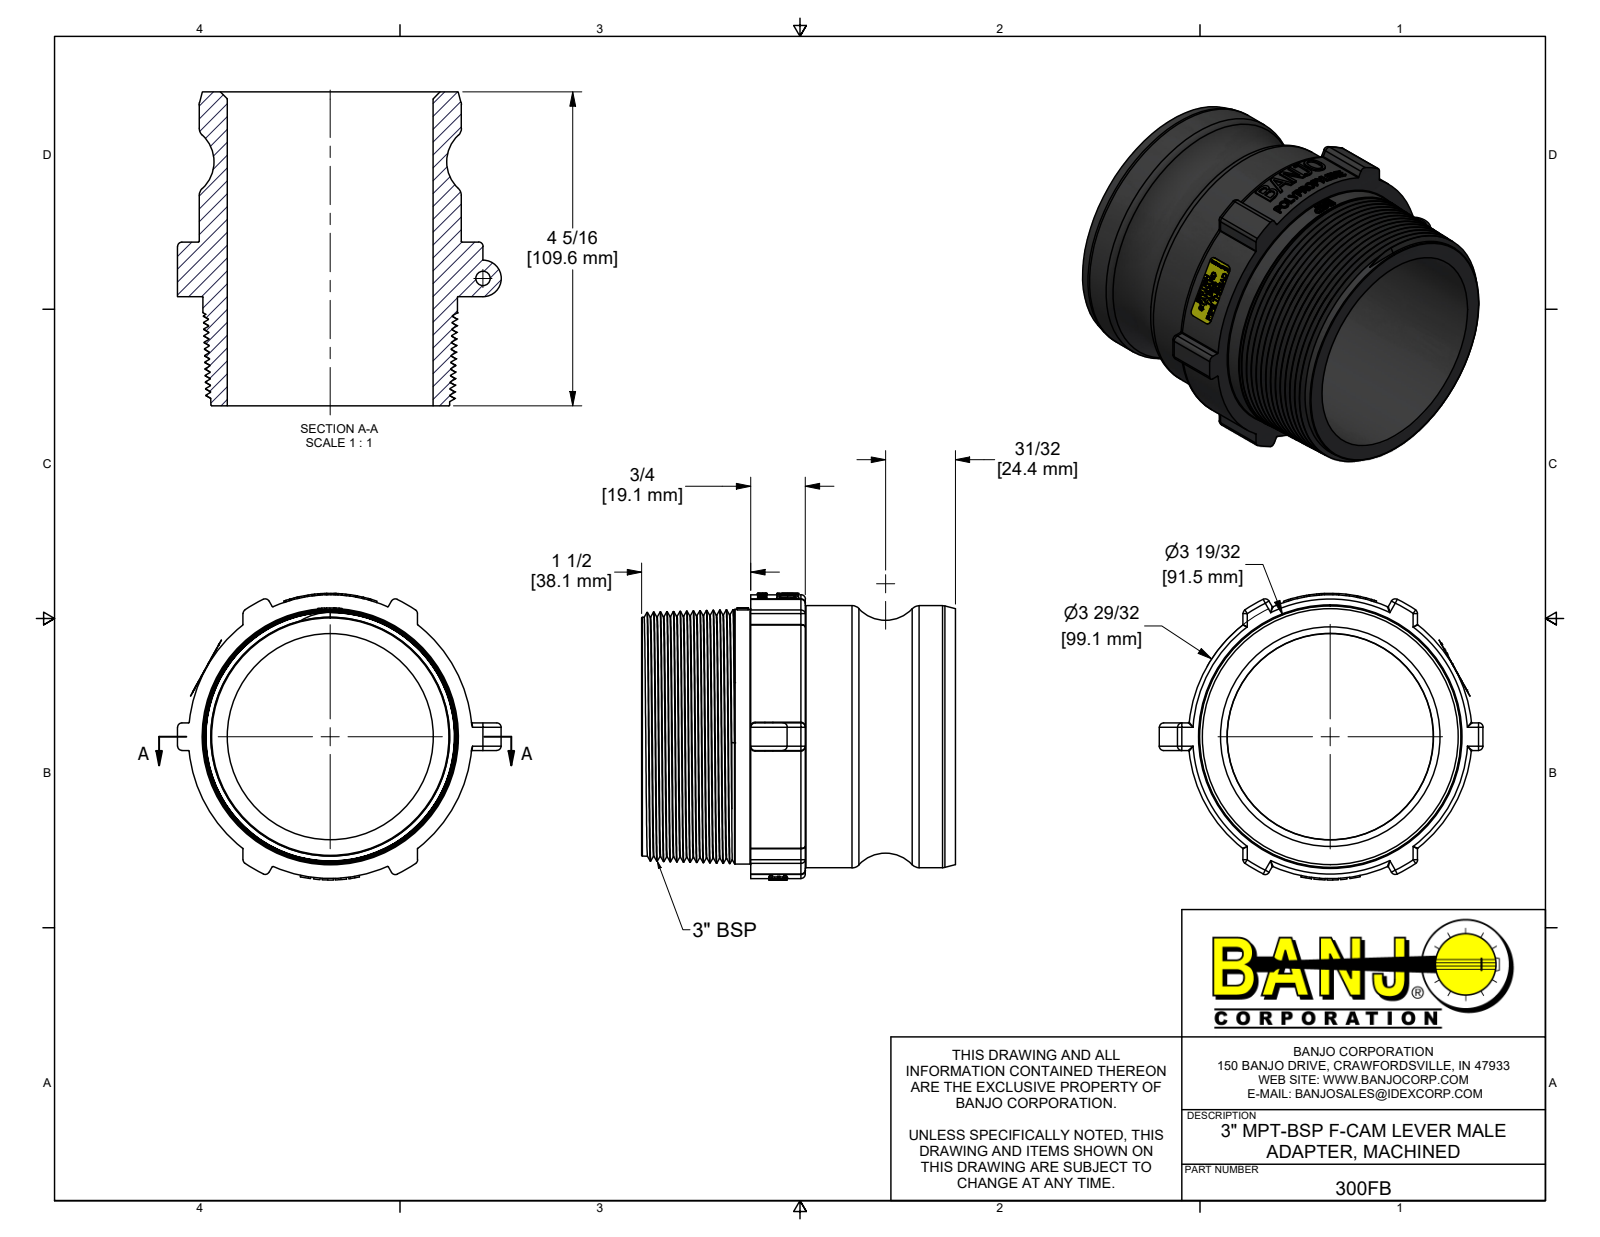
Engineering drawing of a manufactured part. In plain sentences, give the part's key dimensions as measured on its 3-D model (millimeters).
The part is named "300FB; 300FBX; VL1012". Its 3-D file was written by "Autodesk Inventor 2022 (AUTOMOTIVE_DESIGN)". It is 2 solids with 1138 faces: 586 planar, 104 cylindrical and 448 other. Overall it measures 113 by 109.6 by 100.1 millimeters. Its volume is 253 500 cubic millimeters and its surface area 71 100 square millimeters. Round holes: 1 of diameter 5.1, 1 of diameter 71.9. Round bosses or shafts: 1 of diameter 91.5, 1 of diameter 88.9. Partial cylindrical surfaces (rounded edges, fillets, slot ends): 28 of radius 1.5, 12 of radius 0.3, 1 of radius 6.4, 1 of radius 19.8, 1 of radius 45, 1 of radius 49.5, 1 of radius 50, 1 of radius 53.3. The main face-to-face distances are 71.5, 38.1, 109.6, 57.2, 19.1, 52.4, 22.9, 83.8, 61, 10.3.
